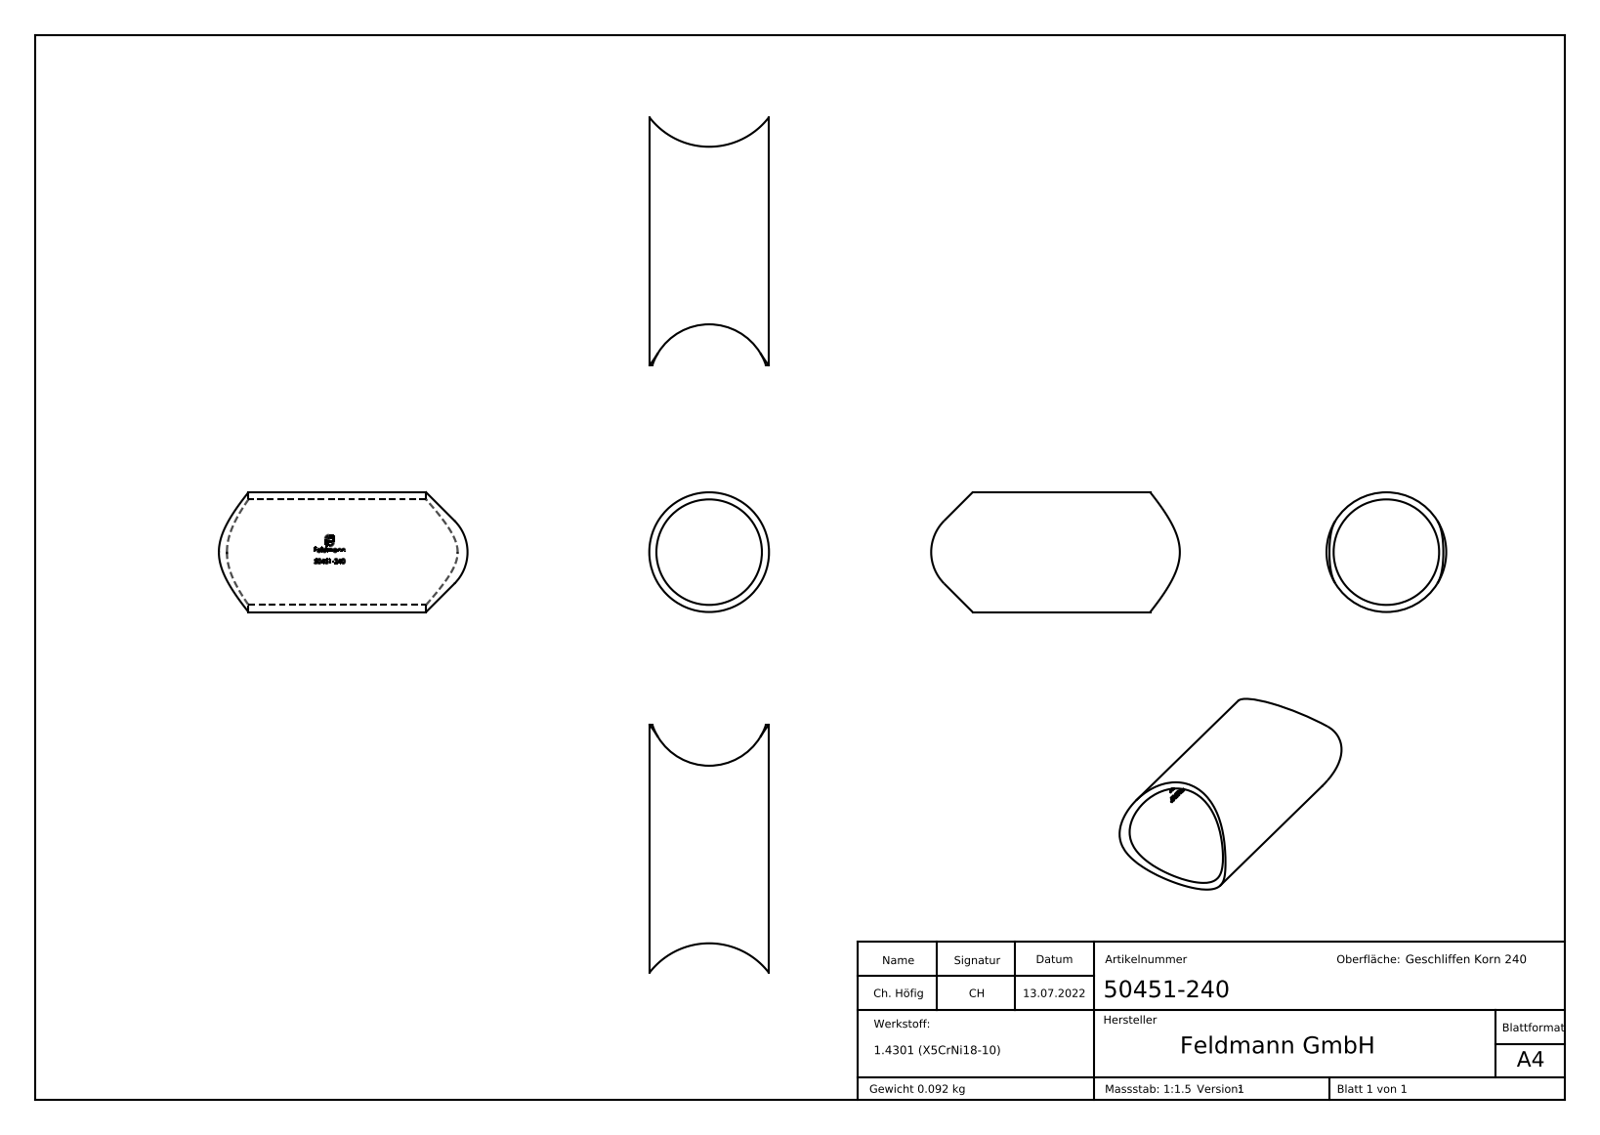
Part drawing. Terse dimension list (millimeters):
name: 50451-240
written by: SolidWorks 2018 (CONFIG_CONTROL_DESIGN)
unit: mm
bodies: 1 solid, 269 faces (130 planar, 31 cylindrical, 108 other)
size: 70 × 33.7 × 33.7
volume: 11 603 mm³; area: 12 145 mm²
holes: 1× ⌀29.7
bosses: 1× ⌀33.7
rounds: 1× R12.52, 1× R14.95, 1× R16.85, 1× R21.2
face distances: 0.88, 2.2, 4.39, 0.68, 1.82, 2.9, 3.2, 3.27, 0.92, 0.34
